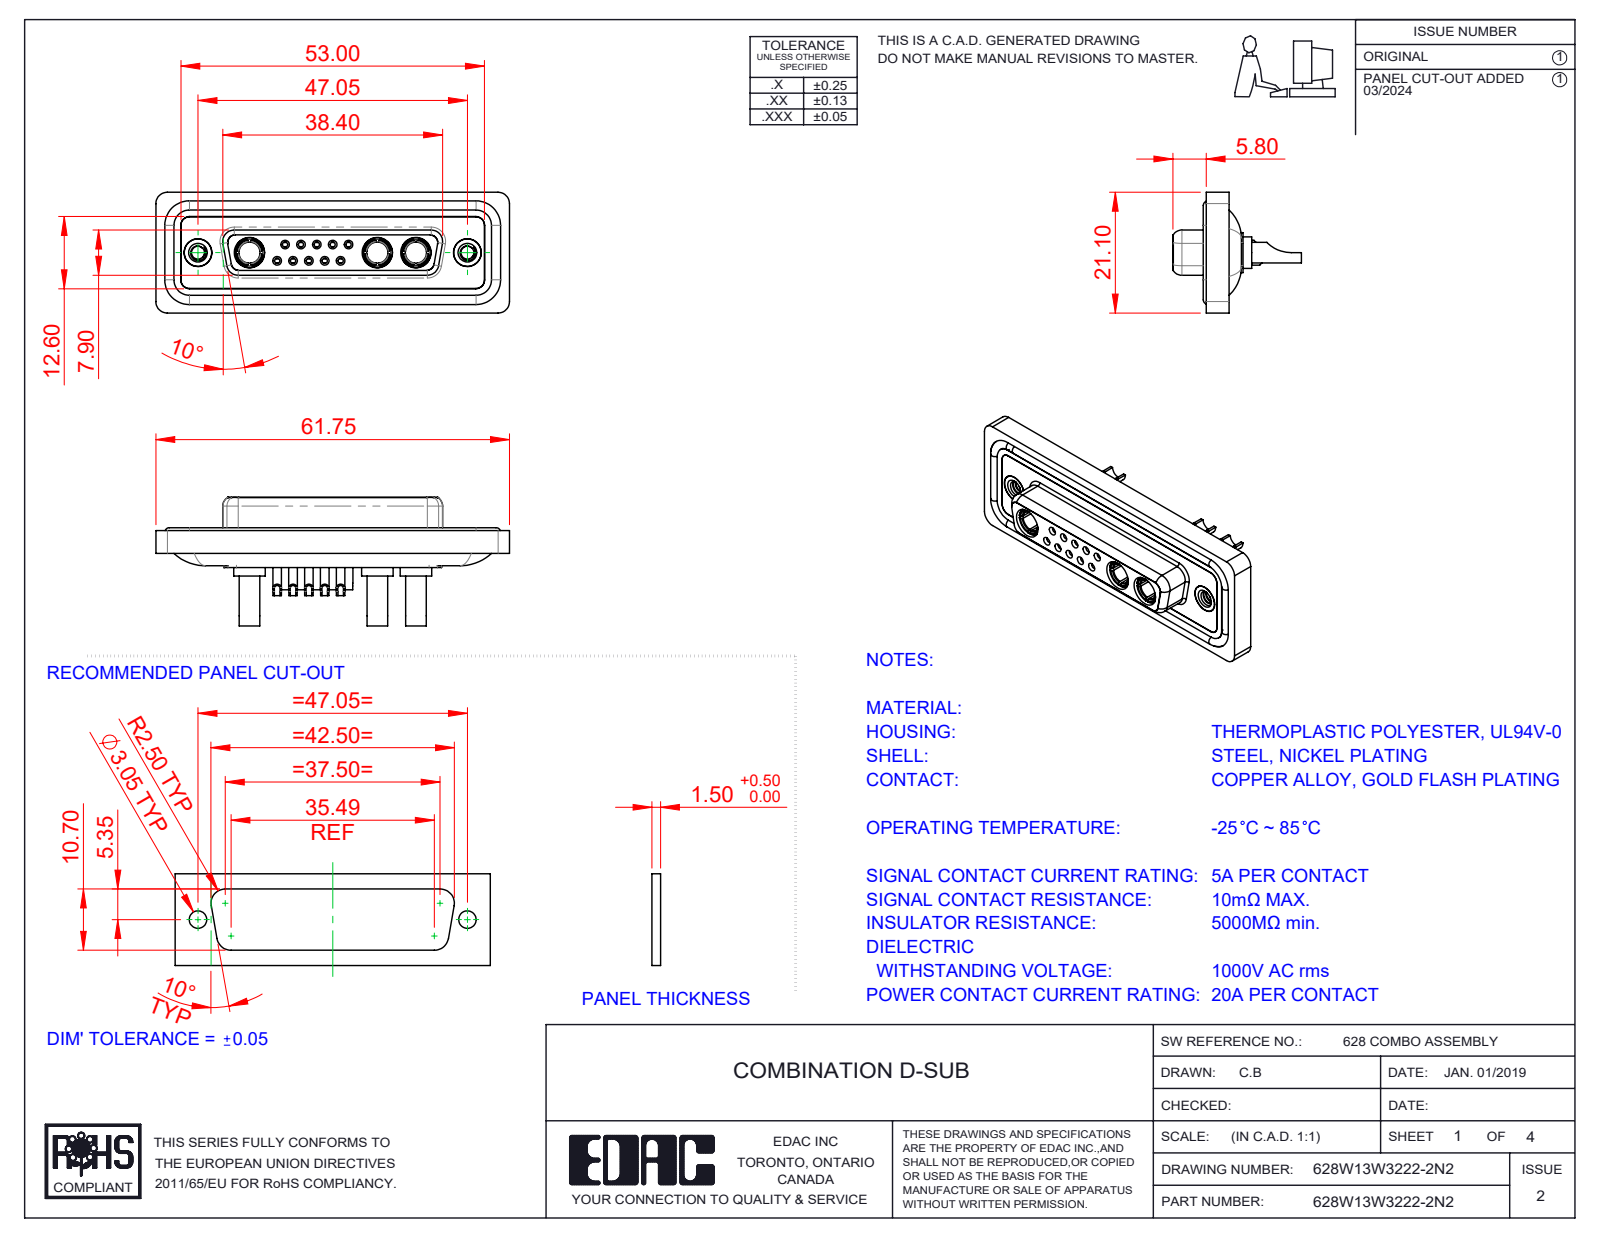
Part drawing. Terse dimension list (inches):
name: 628W13W3222-2N2; 628Combo Shell Front_25 Contacts; 628Combo Shell Rear_25 Contacts; 628Combo Contact Row 2_22 (+5 more)
written by: SolidWorks 2023 (CONFIG_CONTROL_DESIGN)
unit: in
bodies: 23 solids, 1176 faces (371 planar, 476 cylindrical, 329 other)
size: 2.431 × 0.884 × 0.831
volume: 0.508 in³; area: 21.79 in²
holes: 10× ⌀0.035, 10× ⌀0.039, 10× ⌀0.043, 10× ⌀0.059, 10× ⌀0.079, 5× ⌀0.063, 5× ⌀0.067, 5× ⌀0.191, 3× ⌀0.106, 3× ⌀0.146, 3× ⌀0.209, 2× ⌀0.089
bosses: 10× ⌀0.087, 9× ⌀0.063, 3× ⌀0.217, 3× ⌀0.205, 3× ⌀0.195, 3× ⌀0.187, 3× ⌀0.148, 3× ⌀0.142
rounds: 22× R0.059, 18× R0.079, 8× R0.053, 8× R0.063, 6× R0.039, 4× R0.01, 4× R0.02, 4× R0.024
face distances: 0.016, 0.071, 0.293, 0.222, 0.02, 0.26, 0.278, 0.063, 0.114, 0.043
hole spacings: 0.124, 0.109, 0.198, 0.198, 0.218, 0.327, 0.295, 0.109
